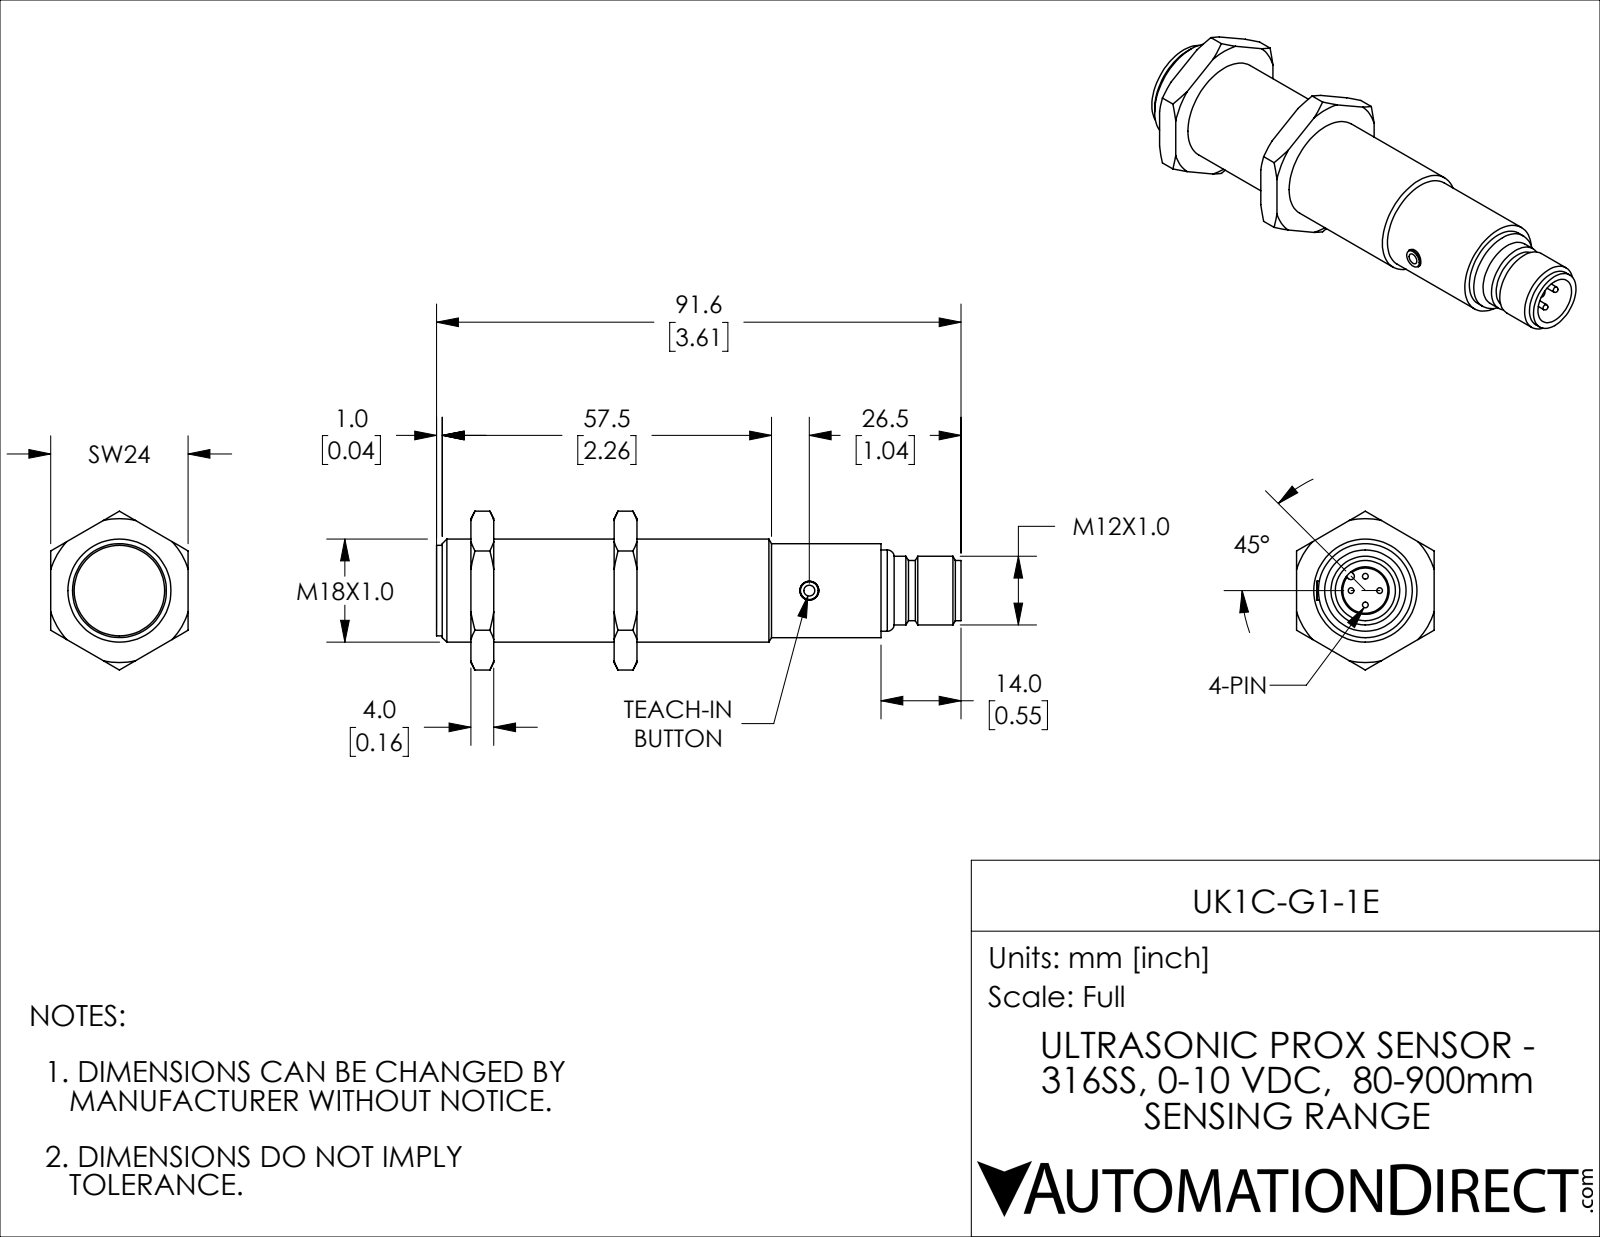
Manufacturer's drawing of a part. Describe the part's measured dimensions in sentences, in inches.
The part is named "UK1C-G1-1E". Its 3-D file was written by "SolidWorks 2018 (AUTOMOTIVE_DESIGN)". It is 4 solids with 113 faces: 27 planar, 35 cylindrical and 51 other. Overall it measures 3.606 by 1.091 by 0.945 inches. Its volume is 1.338 cubic inches and its surface area 11.97 square inches. Round holes: 1 of diameter 0.13, 1 of diameter 0.327, 1 of diameter 0.709. Round bosses or shafts: 4 of diameter 0.039, 1 of diameter 0.646, 1 of diameter 0.622, 1 of diameter 0.559, 1 of diameter 0.472, 1 of diameter 0.413. Partial cylindrical surfaces (rounded edges, fillets, slot ends): 1 of radius 0.024. The main face-to-face distances are 0.984, 0.157, 0.945, 1.142, 0.827, 0.236, 0.394, 1.22, 1.378, 3.055.
